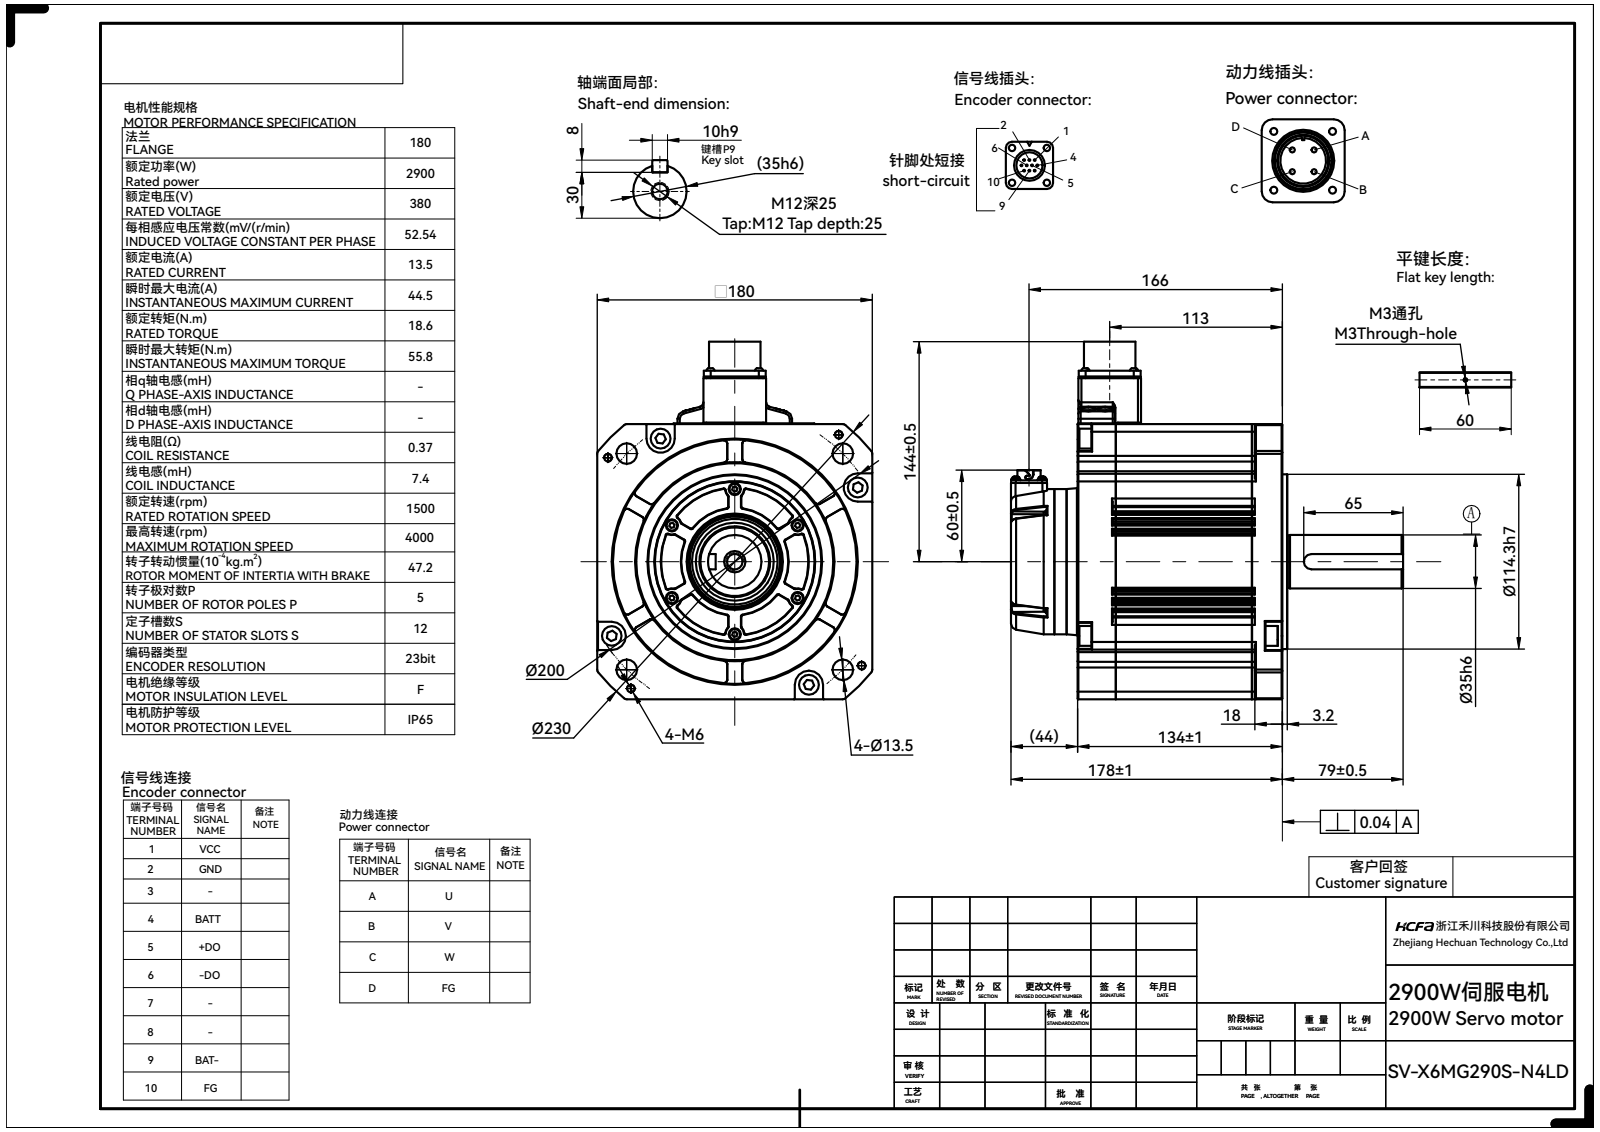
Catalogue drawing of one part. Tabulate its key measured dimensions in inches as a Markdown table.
| quantity | value |
| --- | --- |
| part name | SV-X6MG290S-N4LD（老后盖加新后盖） |
| STEP written by | ZW3D to STEP translator (AUTOMOTIVE_DESIGN) |
| units | inches |
| bodies | 1 solid, 3047 faces (1031 planar, 1030 cylindrical, 986 other) |
| overall size | 10.102 × 9.209 × 7.087 |
| volume | 257.4 in³ |
| surface area | 355.2 in² |
| round holes (diameter × count) | 0.315 × 6, 0.13 × 4, 0.134 × 4, 0.197 × 4, 0.217 × 4, 0.374 × 4, 0.531 × 4, 0.402 × 1, 0.457 × 1, 0.465 × 1, 1.091 × 1, 2.323 × 1 |
| round bosses / shafts (diameter × count) | 0.197 × 8, 0.039 × 8, 0.276 × 6, 0.512 × 4, 0.335 × 4, 0.264 × 4, 0.236 × 4, 0.217 × 4 |
| partial cylindrical surfaces (radius × count) | 0.02 × 88, 0.039 × 52, 0.006 × 48, 0.008 × 26, 0.197 × 25, 0.079 × 20, 0.012 × 16, 0.118 × 14 |
| main face-to-face distances | 7.087, 1.28, 5.807, 5.276, 4.528, 0.157, 5.118, 1.717, 6.992, 6.835 |
| hole center spacings | 1.87, 4.278, 0.496, 0.502, 1.368, 1.673, 2.163, 2.185 |
